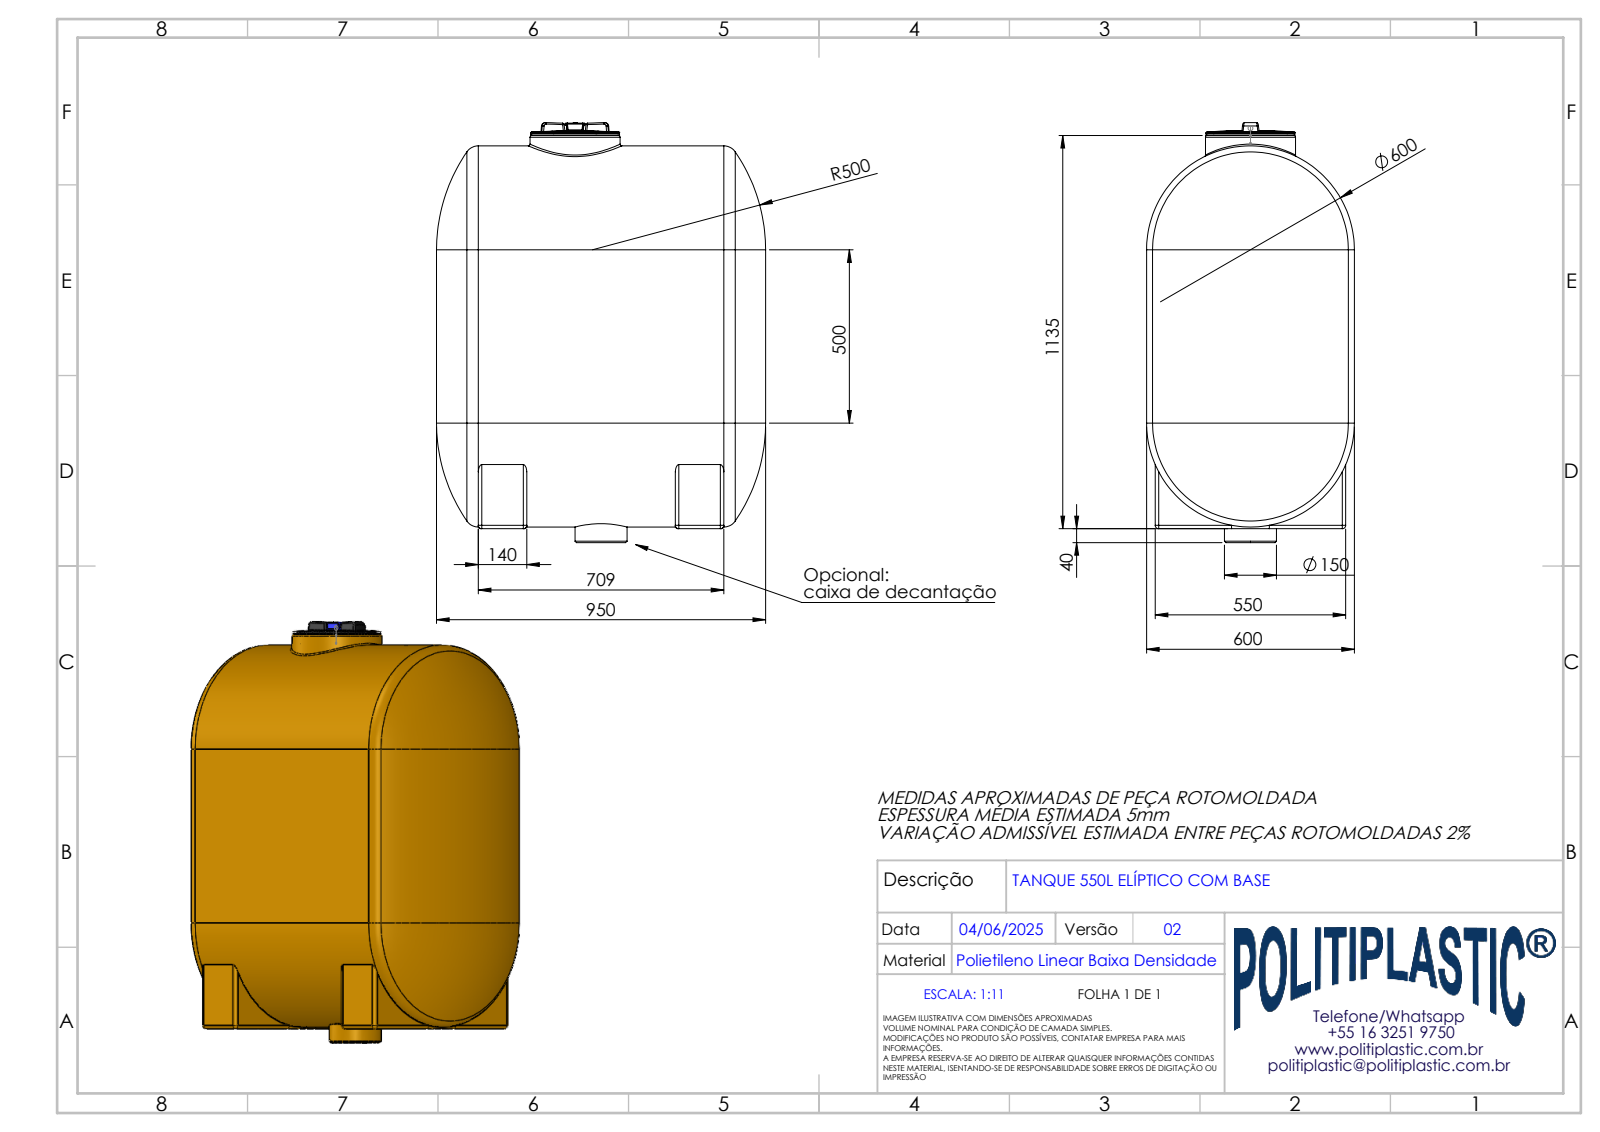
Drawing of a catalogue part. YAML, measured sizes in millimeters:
part_name: "550L TANQUE ELIPTICO COM BASE POLITIPLASTIC; VALVULA; MONTAGEM TAMPA POLITIPLASTIC; TAMPA TRAVA DO FILTRO (+3 more)"
step_written_by: "SolidWorks 2025 (AUTOMOTIVE_DESIGN)"
units: millimeters
bodies: {solids: 11, faces: 6149, planar: 4835, cylindrical: 784, other: 530}
overall_size: [1212.22, 950, 600]
volume: 23280000
surface_area: 7684000
round_holes:
  - {diameter: 4.07, count: 6}
  - {diameter: 10.69, count: 6}
  - {diameter: 17.31, count: 1}
  - {diameter: 49.68, count: 1}
  - {diameter: 61.08, count: 1}
  - {diameter: 148.5, count: 1}
  - {diameter: 189.35, count: 1}
  - {diameter: 199, count: 1}
  - {diameter: 210, count: 1}
  - {diameter: 213.78, count: 1}
  - {diameter: 248, count: 1}
  - {diameter: 248.39, count: 1}
round_bosses_or_shafts:
  - {diameter: 10.69, count: 6}
  - {diameter: 260, count: 1}
  - {diameter: 256.54, count: 1}
  - {diameter: 251.45, count: 1}
  - {diameter: 221.38, count: 1}
  - {diameter: 211.4, count: 1}
  - {diameter: 205.91, count: 1}
  - {diameter: 205.13, count: 1}
partial_cylinders:
  - {radius: 2.04, count: 28}
  - {radius: 10, count: 15}
  - {radius: 2.54, count: 8}
  - {radius: 4, count: 8}
  - {radius: 77.14, count: 8}
  - {radius: 654.13, count: 8}
  - {radius: 0.7, count: 4}
  - {radius: 34, count: 4}
face_to_face_distances: [6, 594, 588, 600, 25, 569, 19, 568.95, 31, 563]
hole_center_spacings: [117.92, 204.24, 118.02, 204.3, 204.35, 204.41, 117.98, 235.84]
